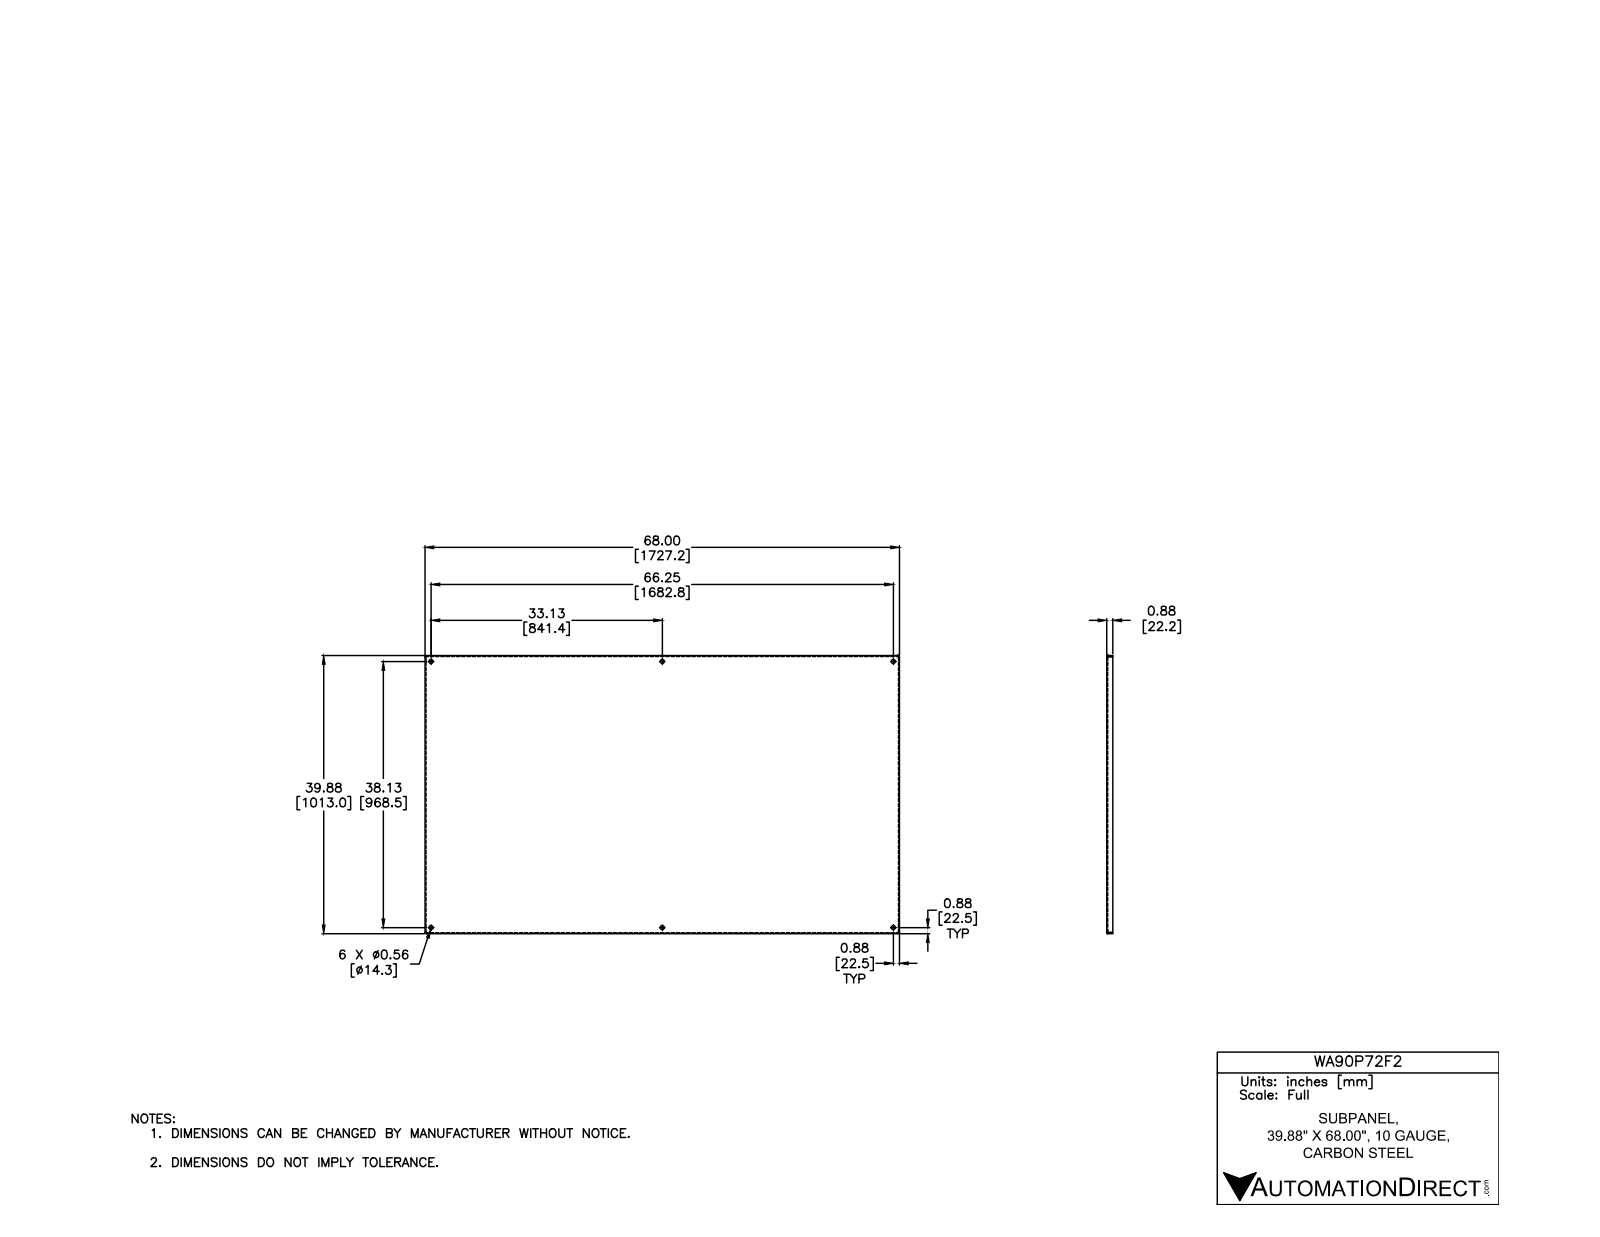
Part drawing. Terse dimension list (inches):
name: WA_P_F
written by: Autodesk Inventor 2012 (AUTOMOTIVE_DESIGN)
unit: in
bodies: 1 solid, 44 faces (22 planar, 14 cylindrical, 8 other)
size: 68 × 39.88 × 0.875
volume: 357.8 in³; area: 5 753 in²
holes: 6× ⌀0.563
rounds: 4× R0.031, 4× R0.156
face distances: 0.125, 0.125, 39.88, 39.755, 39.755, 39.63, 67.875, 67.75, 68, 67.875
hole spacings: 33.125, 33.125, 38.13, 50.509, 66.25, 76.439, 38.13, 50.509
